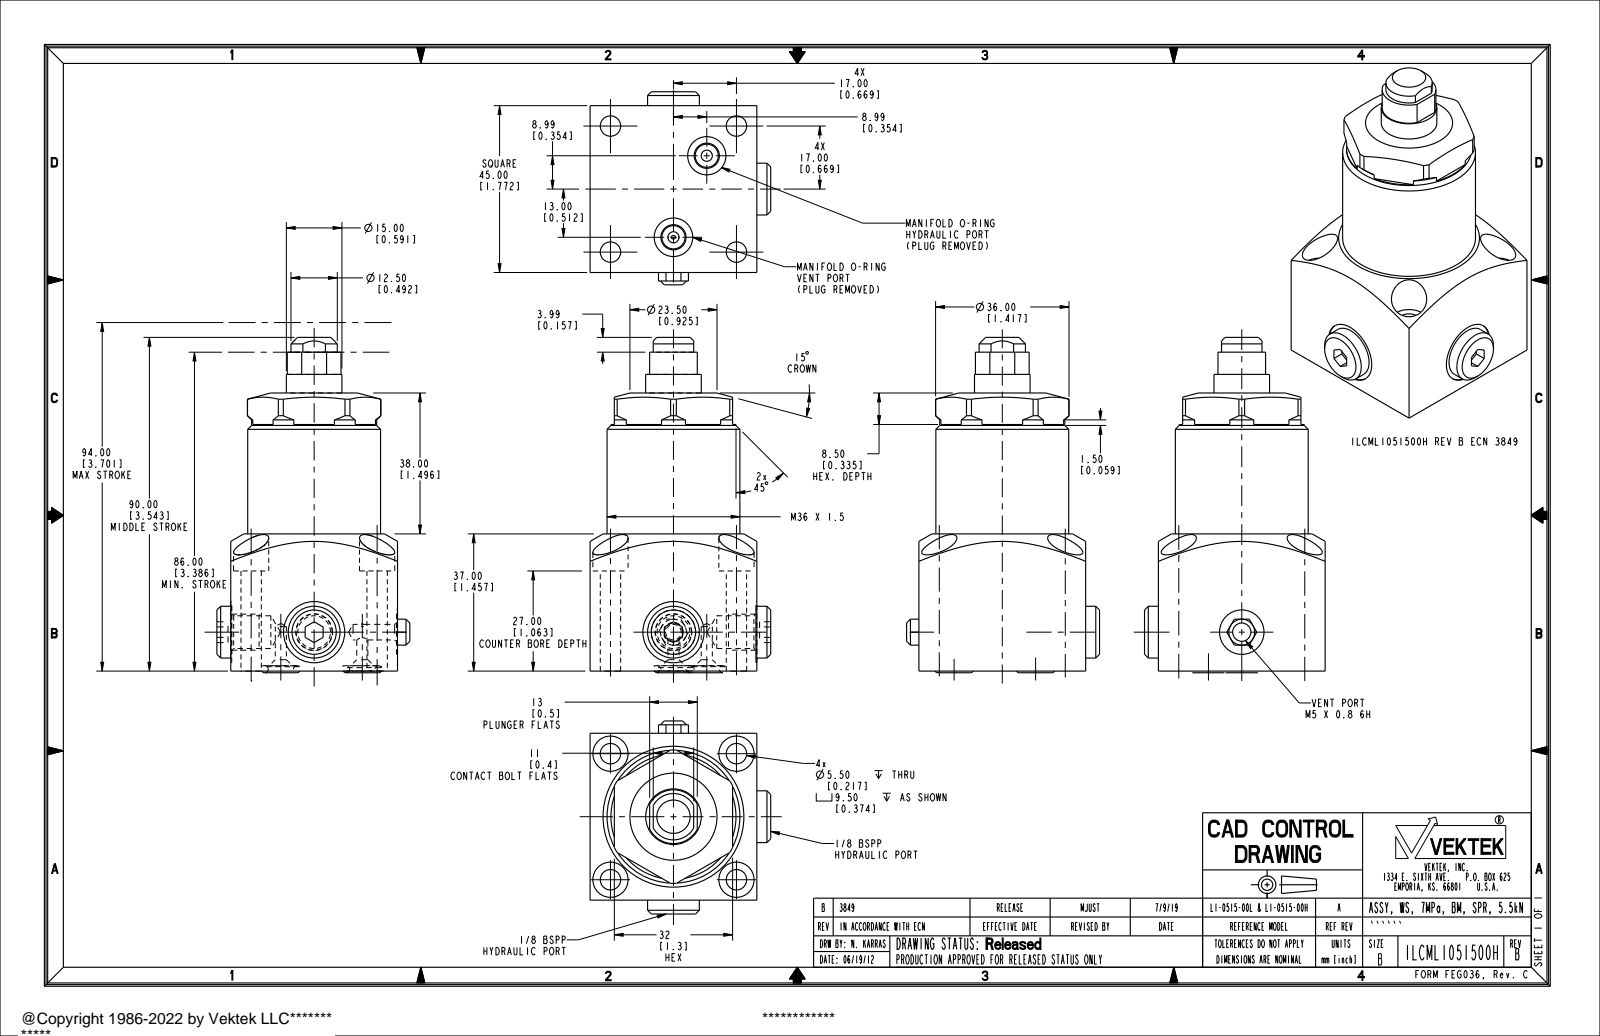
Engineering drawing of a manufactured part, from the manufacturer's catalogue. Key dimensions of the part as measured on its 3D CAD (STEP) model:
Part name (STEP PRODUCT): ILCML1051500H
STEP written by: PRO/ENGINEER BY PARAMETRIC TECHNOLOGY CORPORATION, 2017170 (AUTOMOTIVE_DESIGN)
Units: millimetres
Bodies: 1 solid, 179 faces (69 planar, 64 cylindrical, 46 other)
Overall size (bounding box): 90.45 × 52.07 × 48.75
Volume: 106 584 mm³ · Surface area: 19 793 mm²
Round holes (diameter × count): ⌀5.5 ×4, ⌀9.5 ×4, ⌀3 ×2, ⌀8.84 ×2, ⌀16.51 ×2, ⌀4.2 ×1, ⌀10 ×1, ⌀10.39 ×1, ⌀12 ×1
Round bosses / shafts (diameter × count): ⌀13.97 ×2, ⌀9.73 ×2, ⌀35.85 ×1, ⌀33.75 ×1, ⌀15 ×1
Partial cylindrical surfaces — rounded edges, fillets, slot ends (radius × count): R6.25 ×1, R7.25 ×1, R18 ×1
Main face-to-face distances: 45, 44.75, 31.92, 75, 6.54, 38.46, 27, 48, 48.75, 4
Hole centre spacings: 34, 17.46, 27.2, 34.48, 48.08, 11.33, 23.76, 36.76
